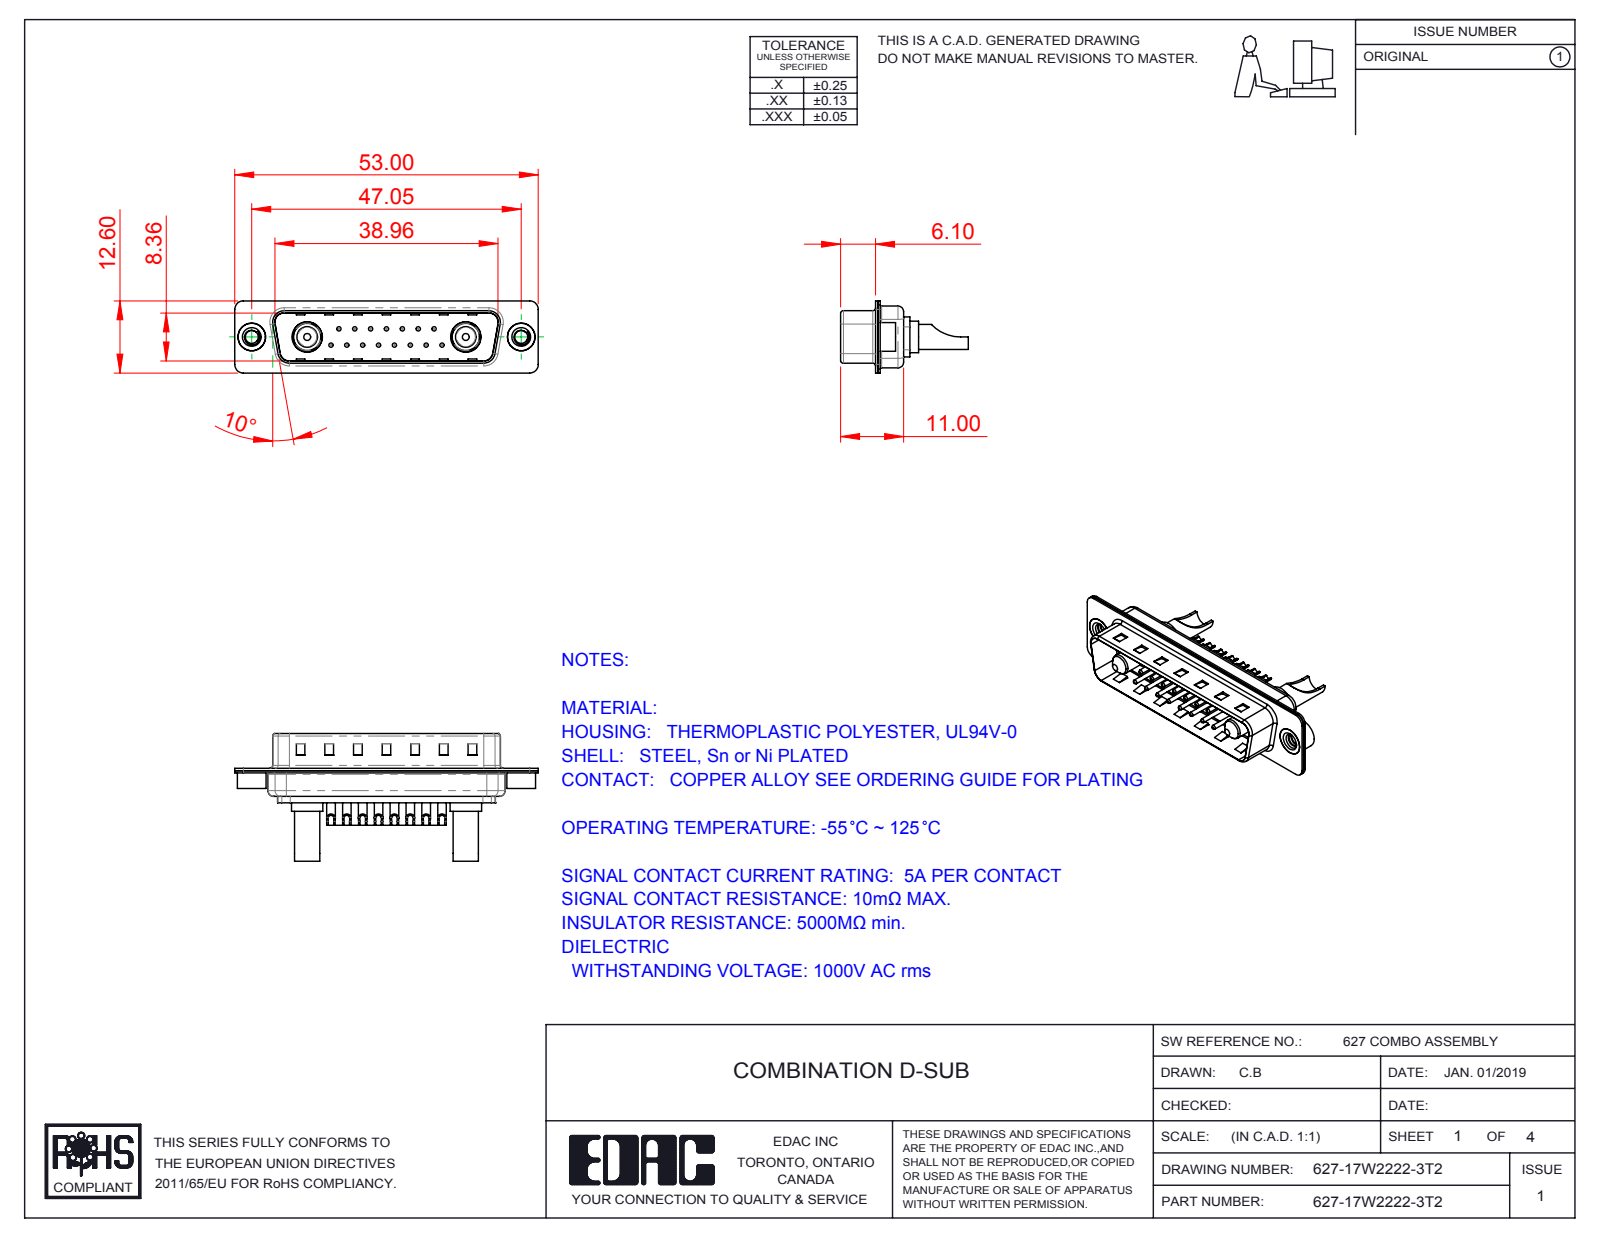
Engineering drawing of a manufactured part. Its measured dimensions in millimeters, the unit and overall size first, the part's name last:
Units: millimetres
Overall size (bounding box): 53 × 22.3 × 12.6
Round holes (diameter × count): ⌀0.75 ×15, ⌀1 ×15, ⌀1.6 ×15, ⌀2 ×15, ⌀2.26 ×2, ⌀3.5 ×2, ⌀4 ×2, ⌀4.8 ×2, ⌀4.85 ×2, ⌀5.3 ×2
Round bosses / shafts (diameter × count): ⌀1.5 ×15, ⌀5.5 ×2, ⌀5.2 ×2, ⌀5 ×2, ⌀4.9 ×2, ⌀4.75 ×2, ⌀4.4 ×2, ⌀3.75 ×2
Partial cylindrical surfaces — rounded edges, fillets, slot ends (radius × count): R1.5 ×16, R2 ×12, R0.5 ×8, R1.6 ×8, R1 ×6, R0.25 ×4, R0.6 ×4, R0.65 ×4
Main face-to-face distances: 0.4, 0.82, 9.58, 8.76, 1.5, 5.6, 5.2, 0.8, 1.22, 9.98
Hole centre spacings: 3.16, 2.77, 5.54, 8.31, 5.04, 7.49, 11.08, 5.03
Volume: 2 927 mm³ · Surface area: 7 123 mm²
Bodies: 24 solids, 1023 faces (332 planar, 421 cylindrical, 270 other)
Part name (STEP PRODUCT): 627Combo Housing_17W2; 627-17W2222-3T2; 627Combo Shell Rear_25 Contacts; 627Combo Shell Front_25 Contacts (+4 more)
STEP written by: SolidWorks 2016 (CONFIG_CONTROL_DESIGN)
